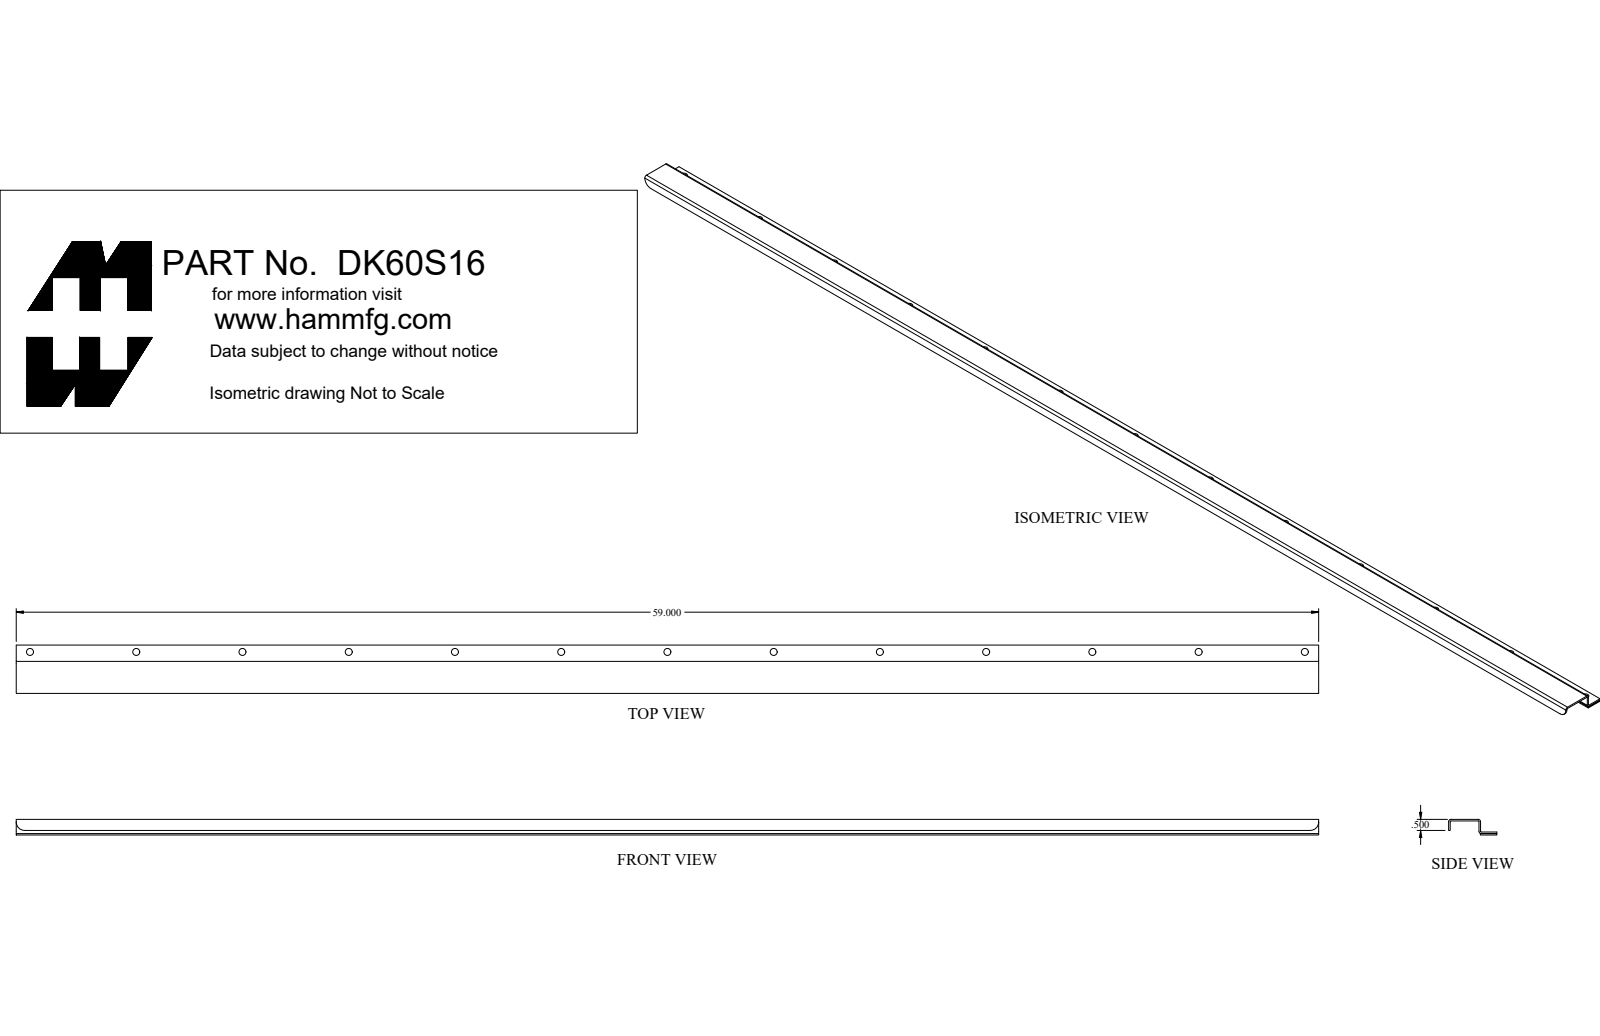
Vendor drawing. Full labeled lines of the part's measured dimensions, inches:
Part name (STEP PRODUCT): DK60S16
STEP written by: SolidWorks 2021 (AUTOMOTIVE_DESIGN)
Units: inches
Bodies: 5 solids, 74 faces (47 planar, 26 cylindrical, 1 other)
Overall size (bounding box): 59 × 2.188 × 1.322
Volume: 15.94 in³ · Surface area: 471.6 in²
Round holes (diameter × count): ⌀0.313 ×13, ⌀0.196 ×1, ⌀0.275 ×1
Round bosses / shafts (diameter × count): ⌀0.625 ×1, ⌀0.483 ×1, ⌀0.25 ×1
Partial cylindrical surfaces — rounded edges, fillets, slot ends (radius × count): R0.036 ×3, R0.108 ×3, R0.375 ×2
Main face-to-face distances: 0.072, 0.572, 0.644, 0.063, 1.376, 0.5, 0.635, 0.707, 0.135, 1.448
Hole centre spacings: 4.813, 14.437, 19.25, 9.625, 33.687, 9.625, 28.875, 4.812
